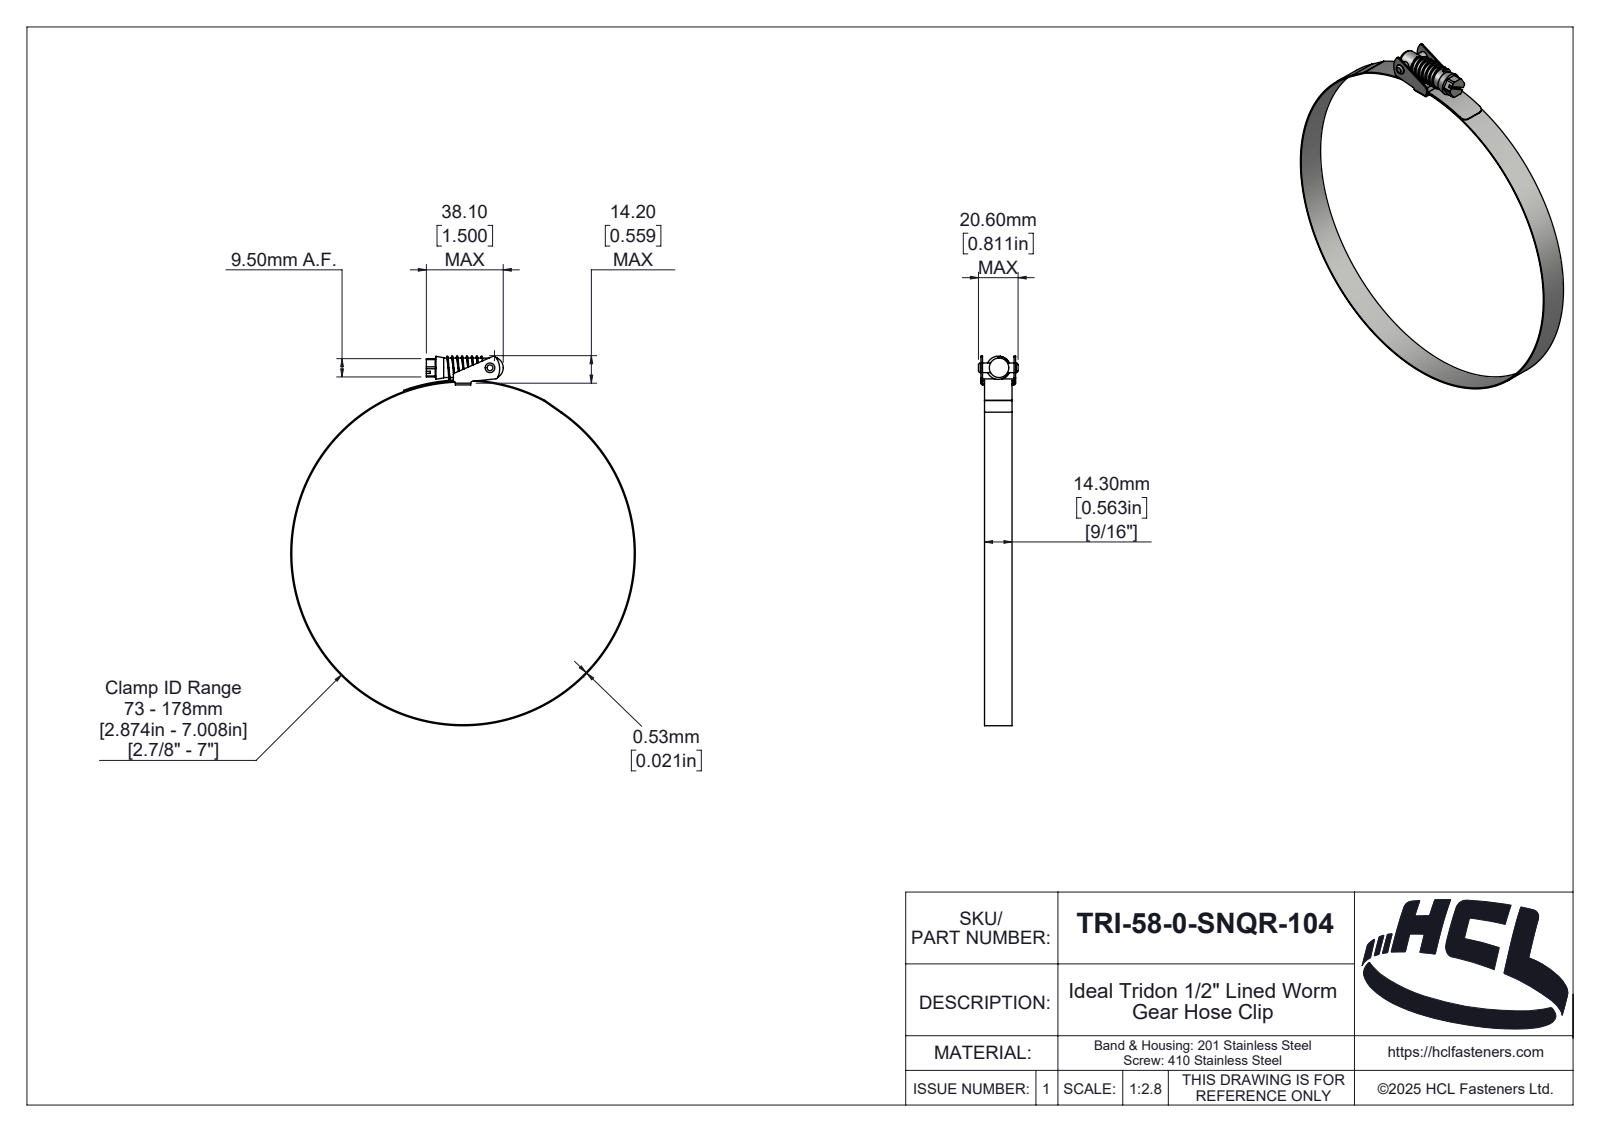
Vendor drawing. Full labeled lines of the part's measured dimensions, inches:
Part name (STEP PRODUCT): TRI-58-0-SNQR-104
STEP written by: SolidWorks 2025 (AUTOMOTIVE_DESIGN)
Units: inches
Bodies: 5 solids, 222 faces (44 planar, 112 cylindrical, 66 other)
Overall size (bounding box): 7.56 × 7.05 × 0.811
Volume: 0.507 in³ · Surface area: 33.36 in²
Round holes (diameter × count): ⌀0.197 ×1, ⌀7.008 ×1
Round bosses / shafts (diameter × count): ⌀7.05 ×1, ⌀0.398 ×1
Partial cylindrical surfaces — rounded edges, fillets, slot ends (radius × count): R0.039 ×11, R0.004 ×2, R0.035 ×2, R0.118 ×2, R0.018 ×1, R0.074 ×1, R0.079 ×1, R0.093 ×1
Main face-to-face distances: 0.031, 0.677, 0.073, 0.636, 0.041, 0.604, 0.563, 0.709, 0.646, 0.021
Hole centre spacings: 3.835
